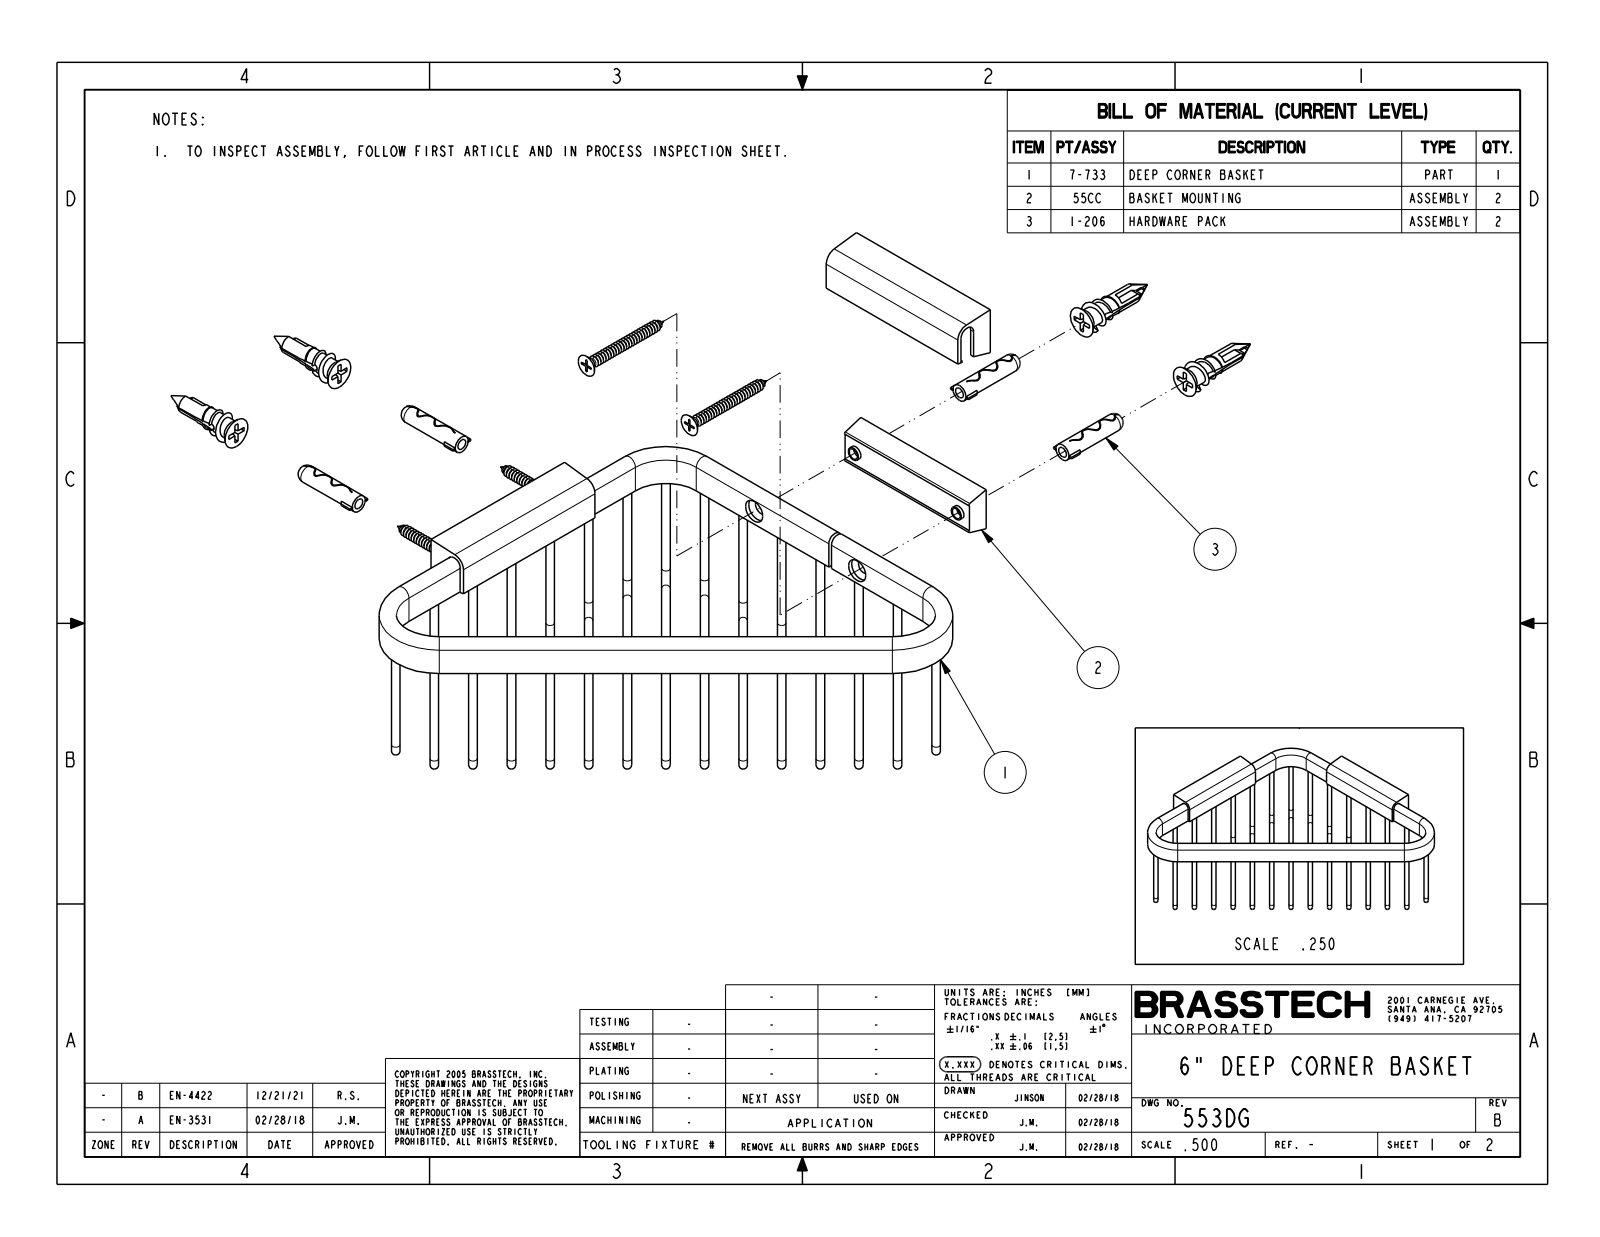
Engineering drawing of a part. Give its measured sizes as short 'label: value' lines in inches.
name: 7-733; 55XX; 55XC; 55CC_ASM (+1 more)
written by: CREO PARAMETRIC BY PTC INC, 2018400 (AUTOMOTIVE_DESIGN)
unit: in
bodies: 5 solids, 322 faces (79 planar, 148 cylindrical, 95 other)
size: 7.874 × 4.764 × 2.387
volume: 3.989 in³; area: 87.62 in²
holes: 4× ⌀0.157, 4× ⌀0.197, 4× ⌀0.209, 4× ⌀0.332
bosses: 45× ⌀0.118
rounds: 5× R0.118, 4× R0.02, 3× R0.591, 3× R0.827, 2× R0.012, 2× R0.177
face distances: 0.236, 0.079, 0.315, 0.059, 0.059, 0.295, 0.551, 0.61, 0.374, 0.08
hole spacings: 2
